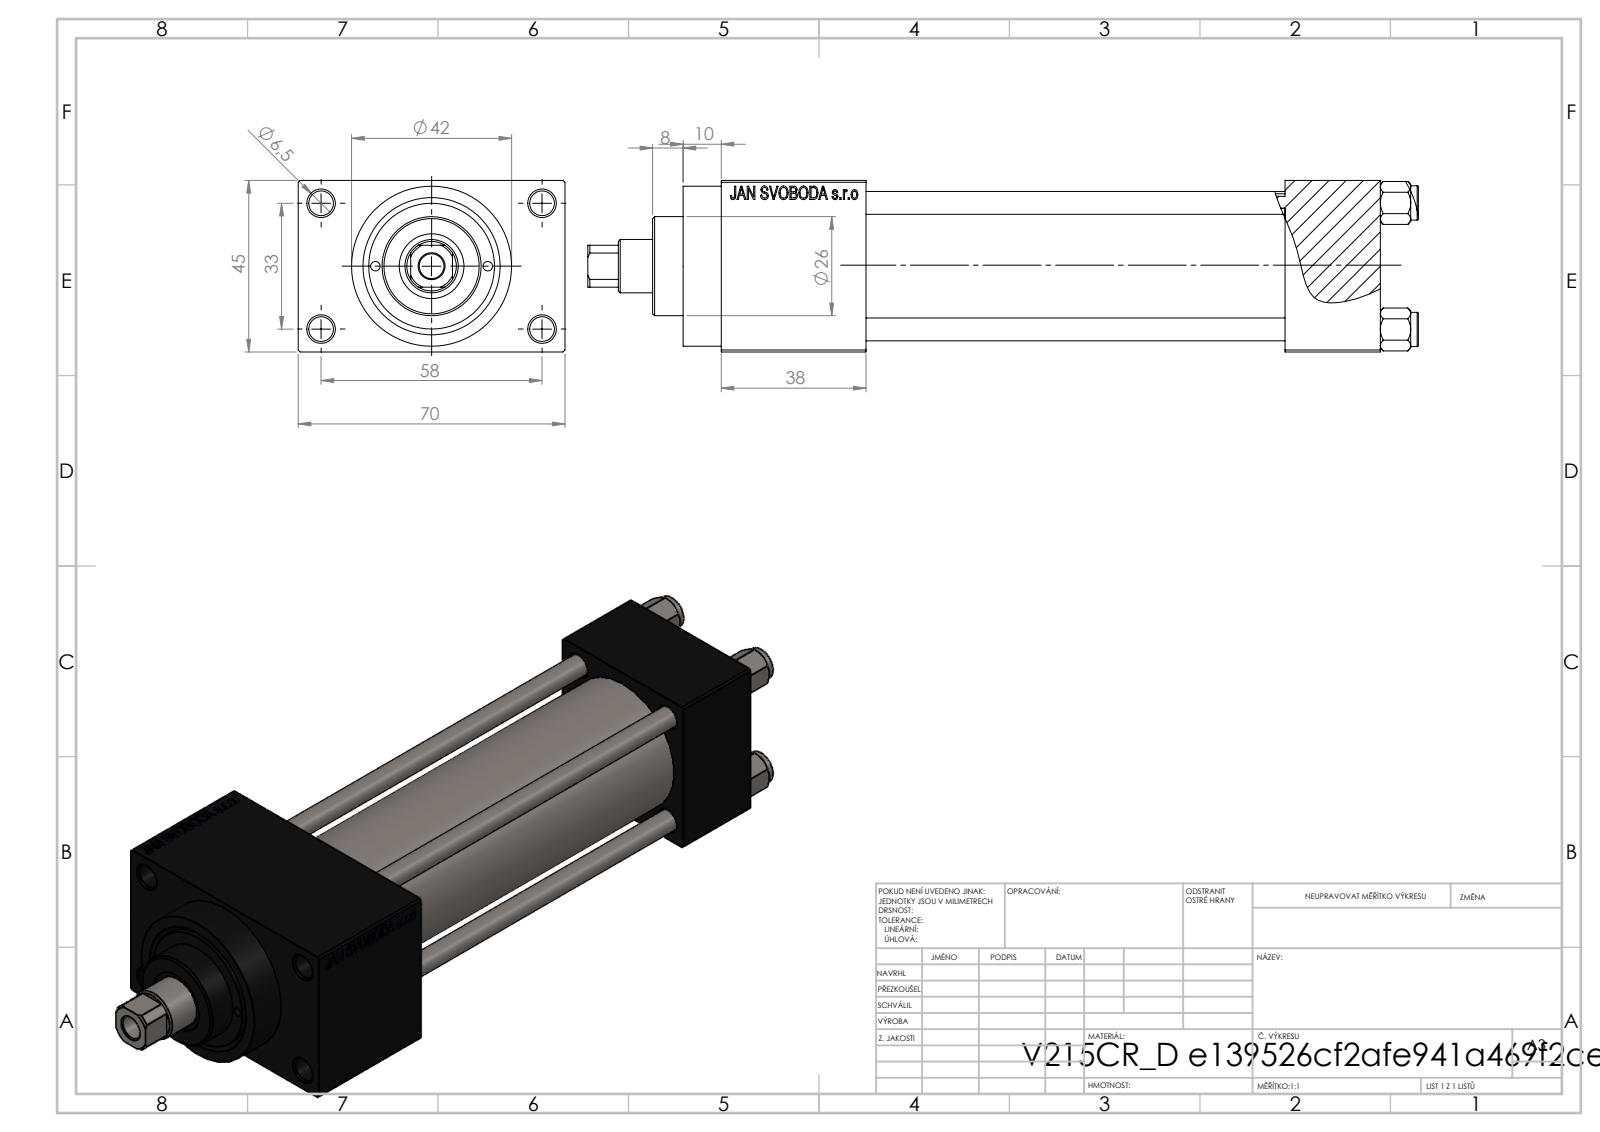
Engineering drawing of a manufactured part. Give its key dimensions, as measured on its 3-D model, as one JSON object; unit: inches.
{"part_name": "V215CR_VCP_D; V215CR_D_TYCINKA; V215_VC_A; V215CR_D_Body (+1 more)", "step_written_by": "SolidWorks 2019 (CONFIG_CONTROL_DESIGN)", "units": "inches", "bodies": {"solids": 11, "faces": 1110, "planar": 498, "cylindrical": 92, "other": 520}, "overall_size": [8.583, 2.756, 1.772], "volume_in3": 16.23, "surface_area_in2": 148.4, "round_holes": [[0.256, 5], [0.236, 4], [0.098, 2], [0.276, 2], [0.518, 2], [0.787, 2], [0.551, 1], [0.669, 1], [0.945, 1], [1.26, 1], [1.299, 1]], "round_bosses_or_shafts": [[0.354, 4], [1.654, 1], [1.496, 1], [1.024, 1]], "partial_cylinders_radius": [[0.256, 1]], "face_to_face_distances": [1.772, 0.984, 0.492, 4.331, 5.315, 2.264, 5.827, 1.496, 6.811, 2.756], "hole_center_spacings": [0.488, 0.657, 0.858, 0.924, 1.307, 1.314, 1.392, 1.396]}
